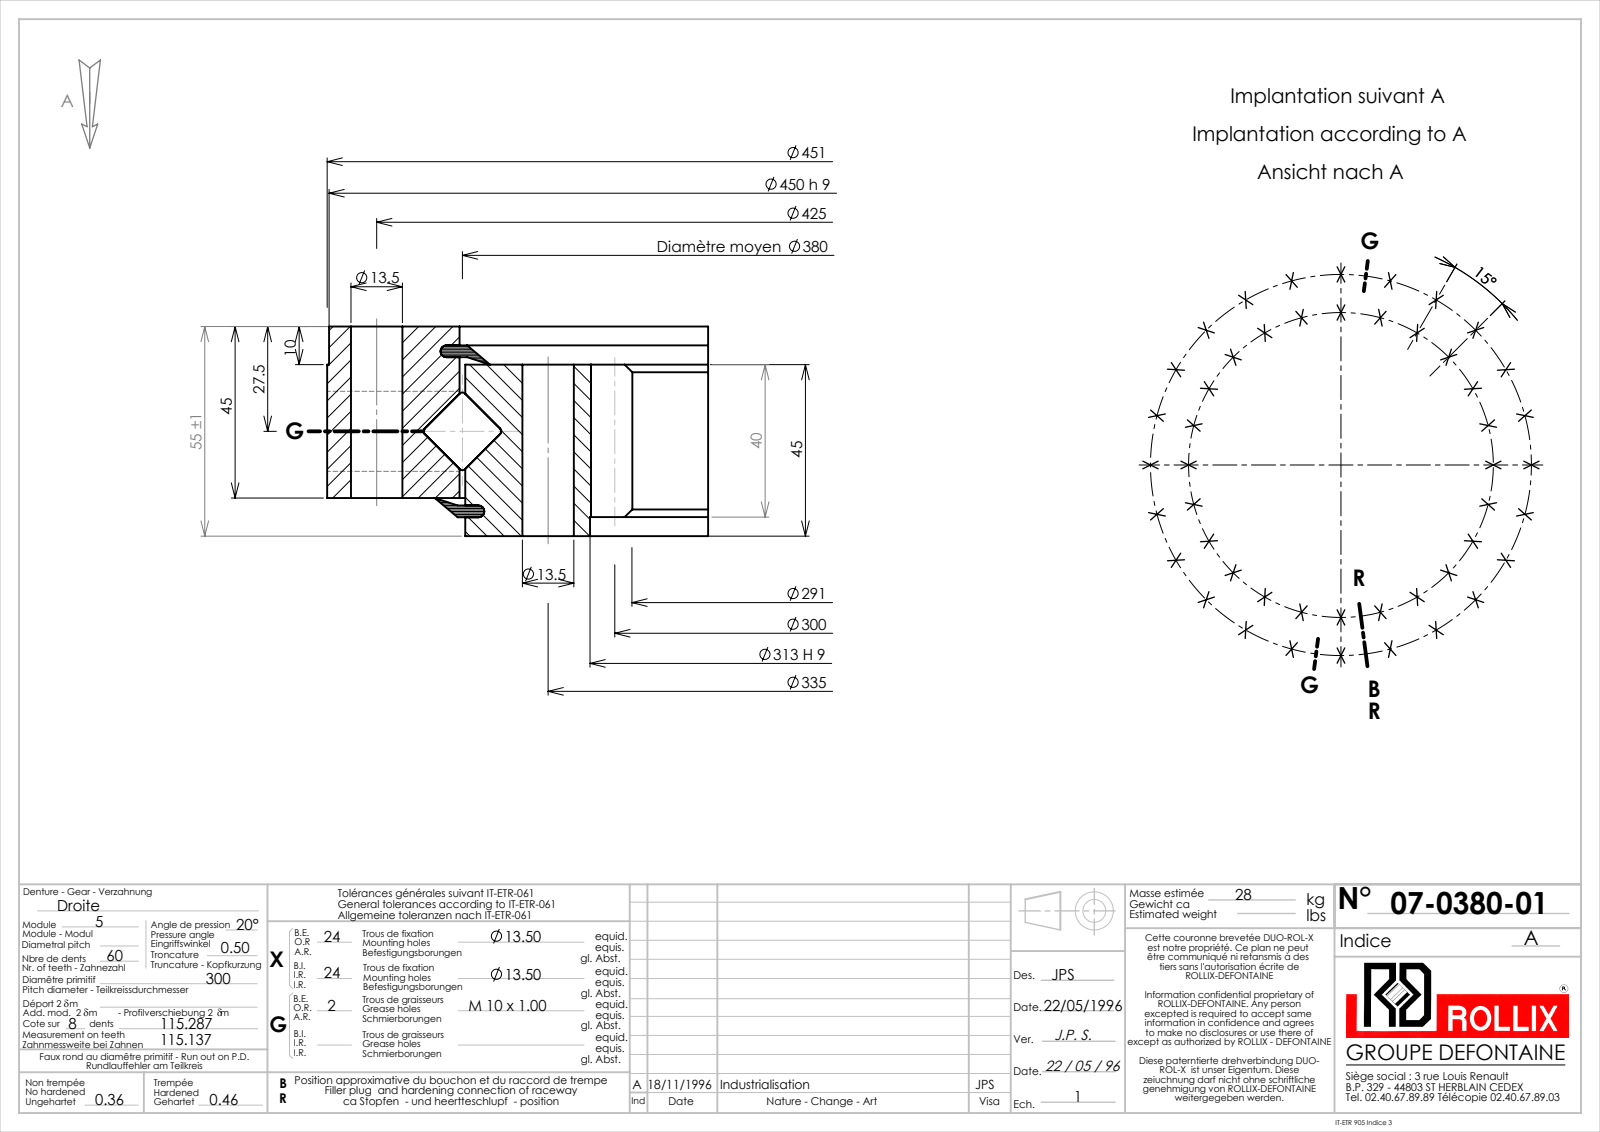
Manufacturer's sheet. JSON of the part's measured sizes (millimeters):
{"part_name": "07-0380-01", "step_written_by": "SolidWorks 2016 (CONFIG_CONTROL_DESIGN)", "units": "millimeters", "bodies": {"solids": 5, "faces": 536, "planar": 136, "cylindrical": 241, "other": 159}, "overall_size": [451, 451, 55], "volume_mm3": 3364000, "surface_area_mm2": 612467, "round_holes": [[13.5, 48], [9, 2], [313, 1], [381.5, 1]], "round_bosses_or_shafts": [[451, 1], [450, 1], [378.5, 1], [15, 1]], "partial_cylinders_radius": [[145.5, 1], [156.25, 1]], "face_to_face_distances": [45, 10, 35, 55, 4.95, 50.05, 5.05, 40.05, 8.05, 46.95], "hole_center_spacings": [167.5, 128.2, 203.93, 236.88, 265.77, 309.5, 332.13, 86.7]}
